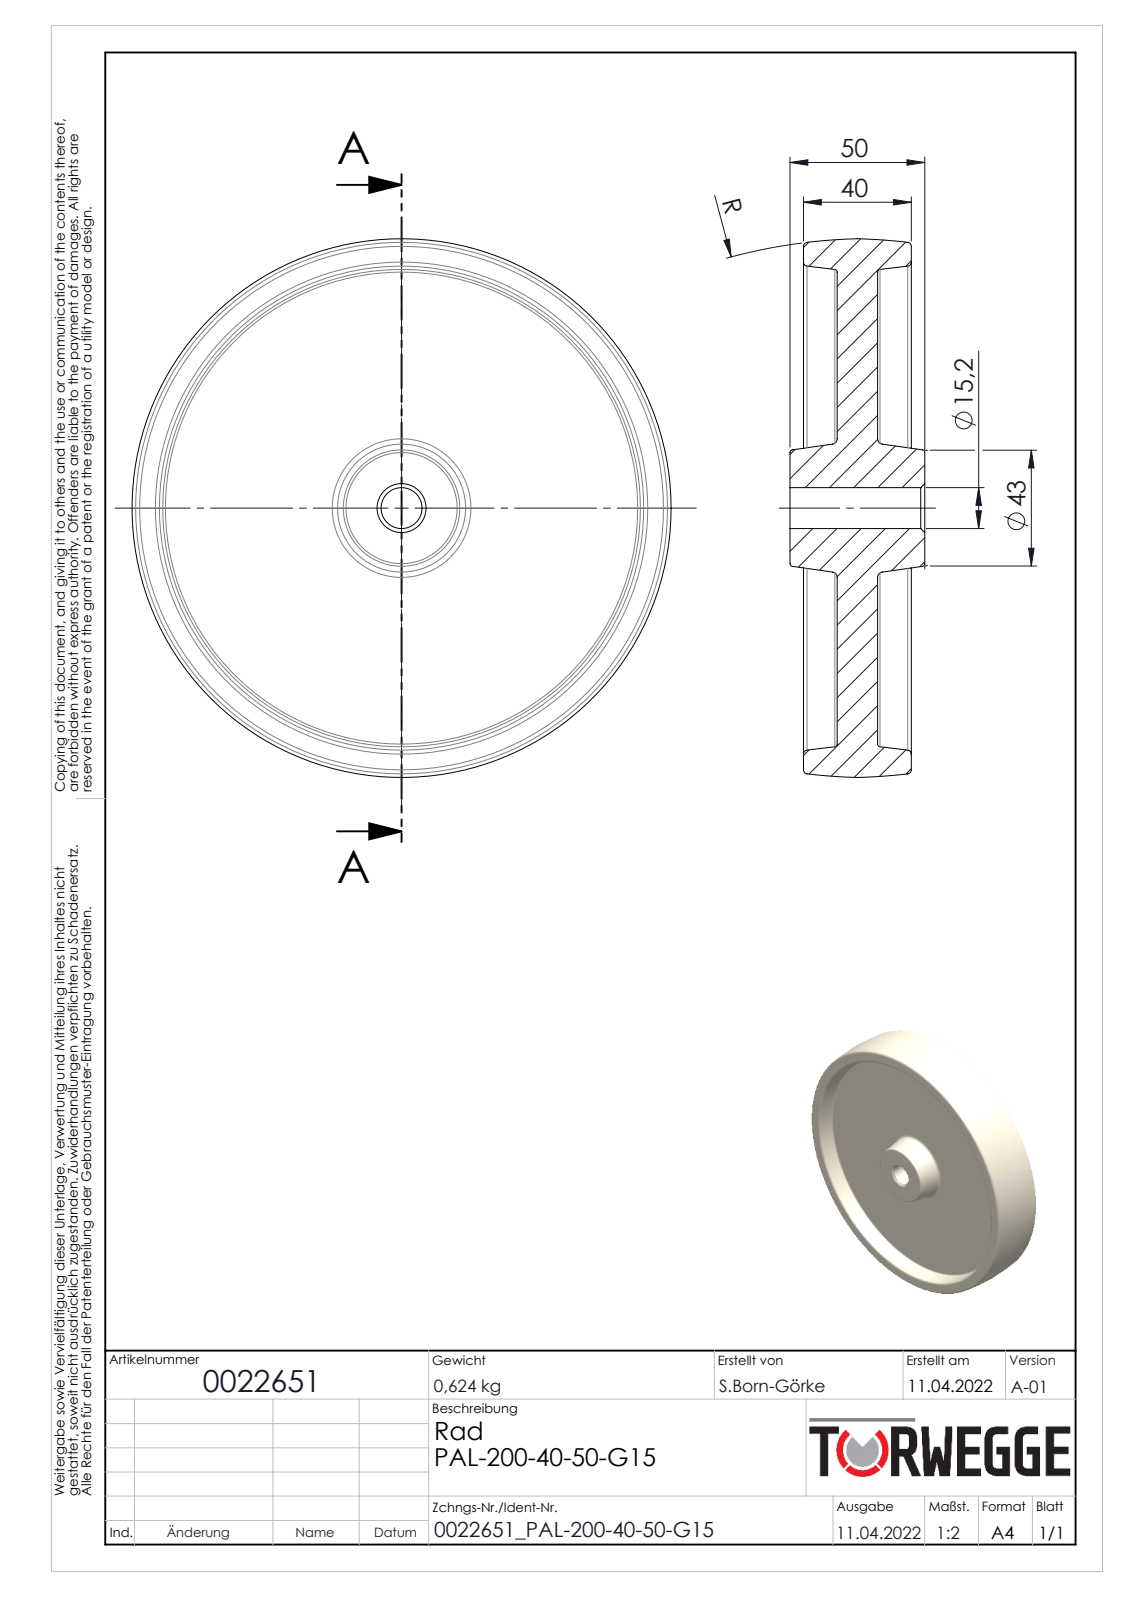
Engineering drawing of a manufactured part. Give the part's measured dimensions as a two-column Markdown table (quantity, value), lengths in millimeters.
| quantity | value |
| --- | --- |
| part name | 0022651 |
| STEP written by | SolidWorks 2020 (AUTOMOTIVE_DESIGN) |
| units | millimeters |
| bodies | 1 solid, 42 faces (6 planar, 2 cylindrical, 34 other) |
| overall size | 200 × 200 × 50 |
| volume | 663 755 mm³ |
| surface area | 103 021 mm² |
| round holes (diameter × count) | 15.2 × 1 |
| main face-to-face distances | 15, 12.5, 27.5, 40, 5, 17.5, 32.5, 45, 50 |
